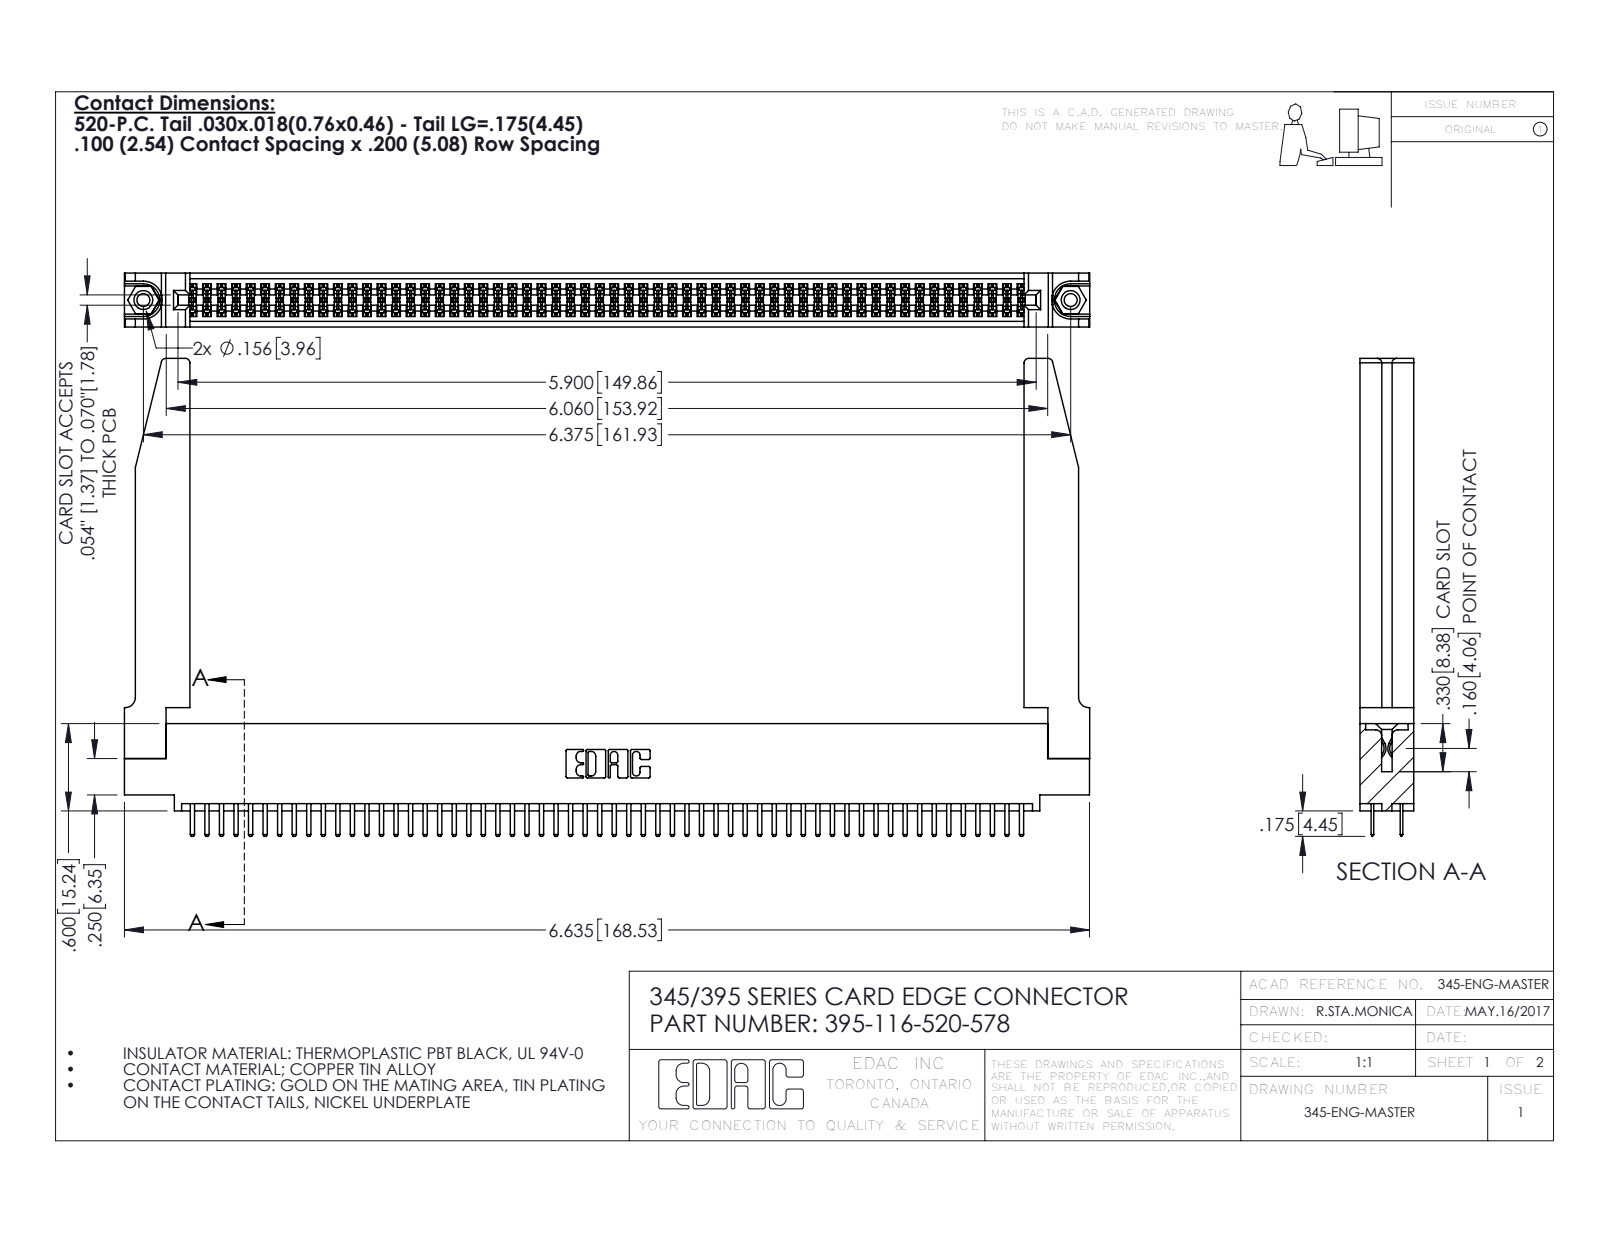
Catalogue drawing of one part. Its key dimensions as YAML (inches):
part_name: "345 Part_0.110 Offset - 0.156 Dia-TH; 345-250-001_345-250-001-102; 345-292-001_345-293-120; 345-220-078_345-220-078 (+1 more)"
step_written_by: "SolidWorks 2016 (CONFIG_CONTROL_DESIGN)"
units: inches
bodies: {solids: 121, faces: 6628, planar: 4286, cylindrical: 2290, other: 52}
overall_size: [6.636, 3.285, 0.37]
volume: 1.475
surface_area: 48.63
round_holes:
  - {diameter: 0.089, count: 2}
  - {diameter: 0.125, count: 2}
  - {diameter: 0.156, count: 2}
  - {diameter: 0.064, count: 1}
round_bosses_or_shafts:
  - {diameter: 0.155, count: 2}
partial_cylinders:
  - {radius: 0.006, count: 174}
  - {radius: 0.01, count: 120}
  - {radius: 0.01, count: 22}
  - {radius: 0.03, count: 8}
  - {radius: 0.007, count: 6}
  - {radius: 0.031, count: 6}
  - {radius: 0.026, count: 3}
  - {radius: 0.014, count: 2}
face_to_face_distances: [0.072, 0.37, 0.298, 0.2, 0.098, 0.272, 0.025, 0.225, 0.022, 0.072]
hole_center_spacings: [0.27, 6.139, 6.375]
